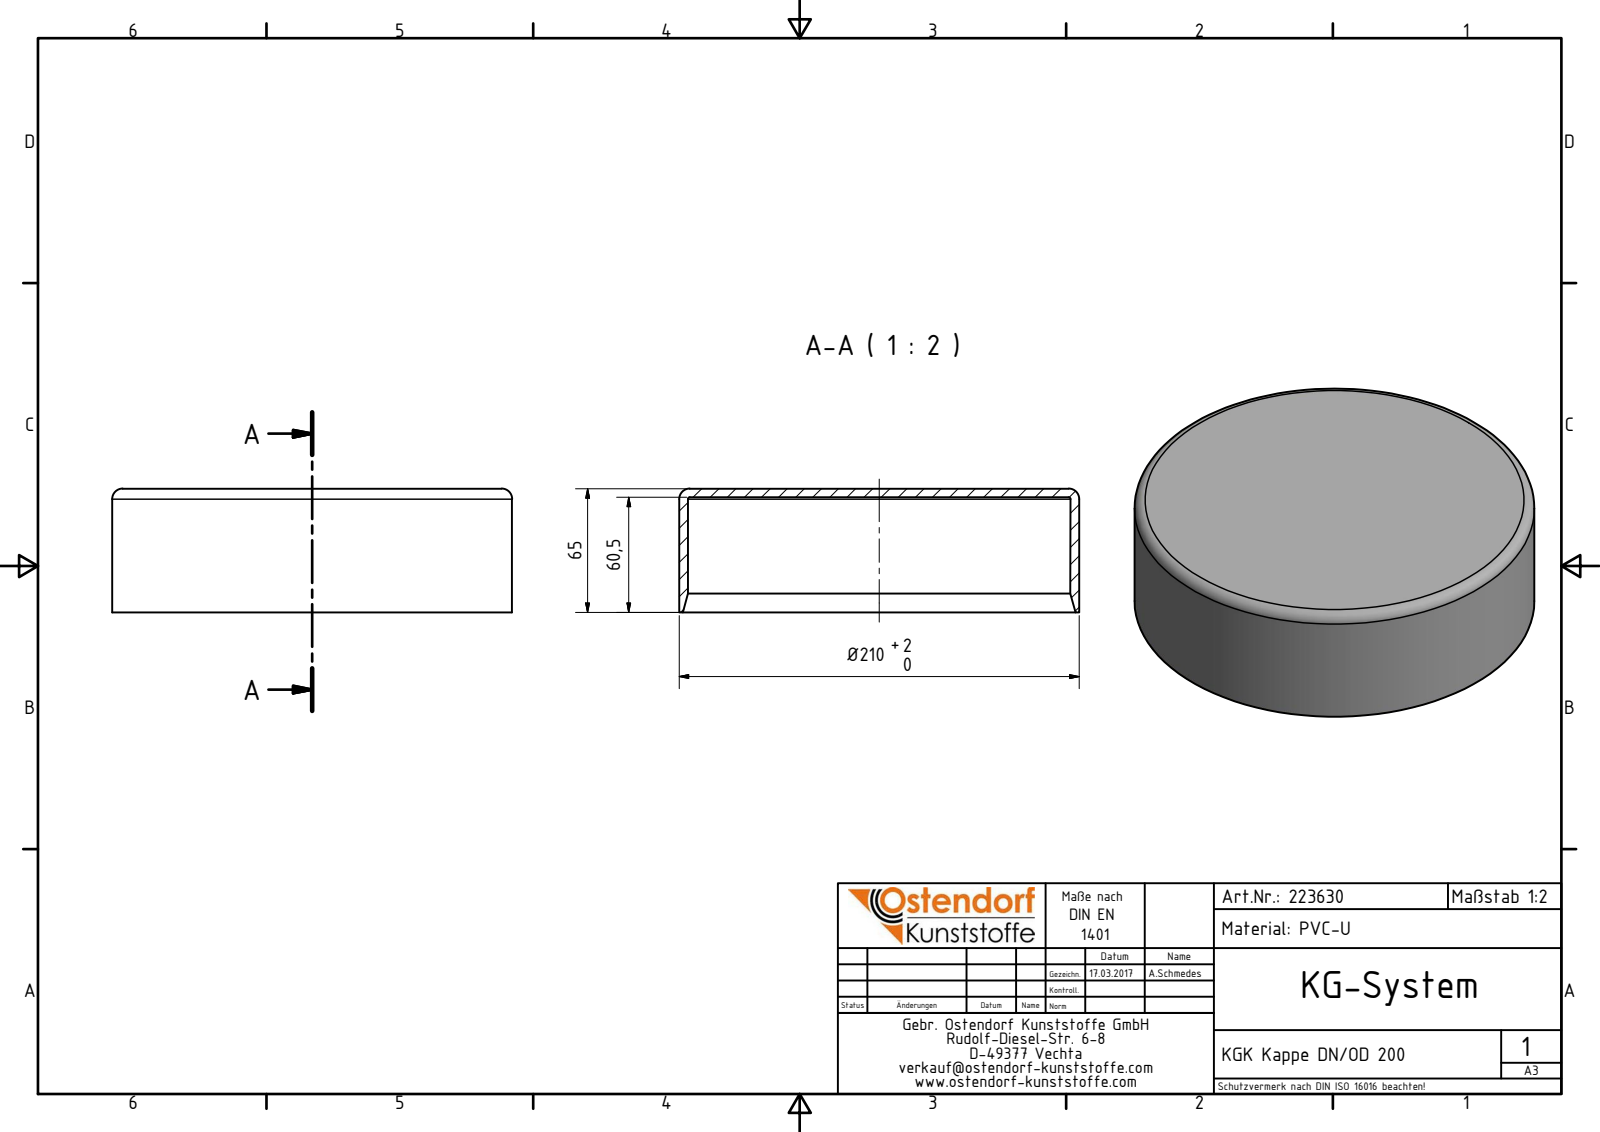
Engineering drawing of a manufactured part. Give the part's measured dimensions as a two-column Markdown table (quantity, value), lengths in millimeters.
| quantity | value |
| --- | --- |
| part name | 223630 KGK Kappe DN_OD 200 |
| STEP written by | Autodesk Inventor 2016 (AUTOMOTIVE_DESIGN) |
| units | millimeters |
| bodies | 1 solid, 8 faces (3 planar, 1 cylindrical, 4 other) |
| overall size | 210 × 210 × 65 |
| volume | 321 228 mm³ |
| surface area | 147 152 mm² |
| round bosses / shafts (diameter × count) | 210 × 1 |
| main face-to-face distances | 4.5, 60.5, 65 |
